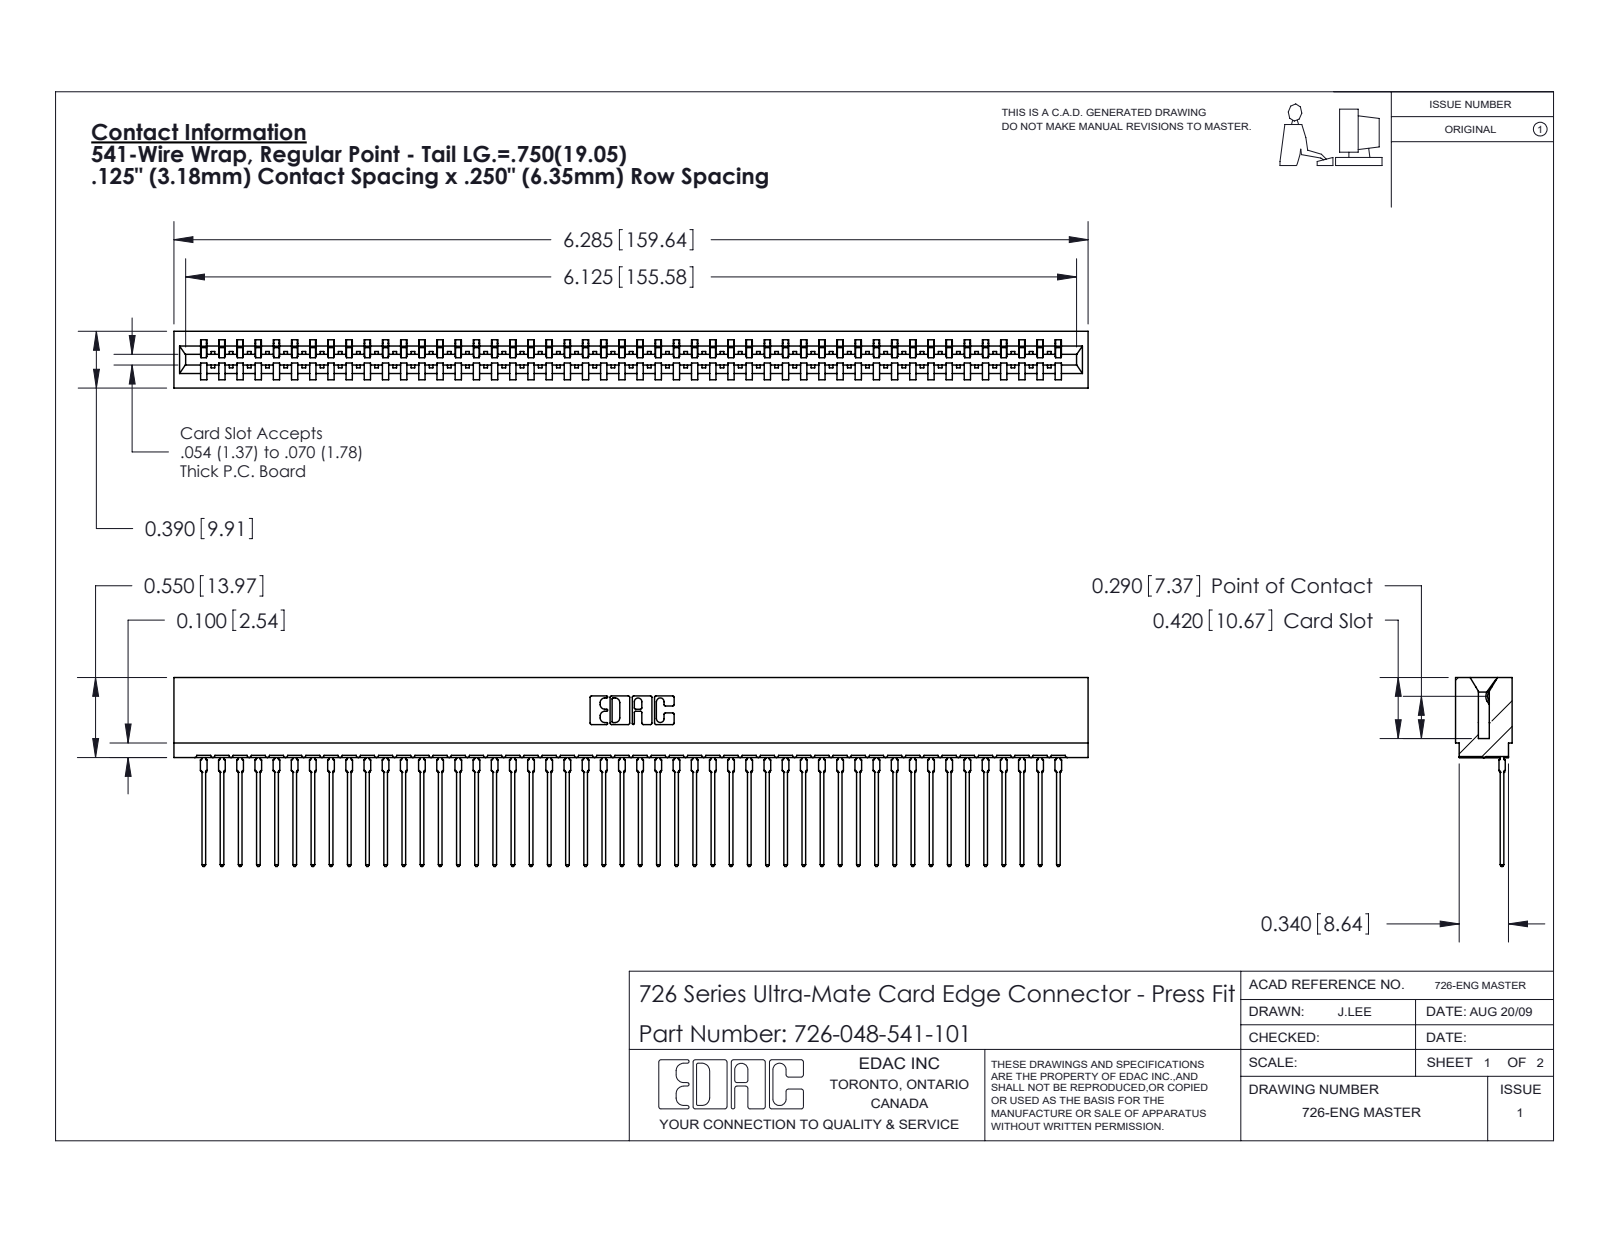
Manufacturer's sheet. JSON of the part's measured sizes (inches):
{"part_name": "726 Part_.515 Slot Depth - 01; 726-048-541-101; 746-292-001_541", "step_written_by": "SolidWorks 2020 (CONFIG_CONTROL_DESIGN)", "units": "inches", "bodies": {"solids": 49, "faces": 5281, "planar": 3079, "cylindrical": 954, "other": 1248}, "overall_size": [6.285, 1.299, 0.39], "volume_in3": 0.882, "surface_area_in2": 36.09, "partial_cylinders_radius": [[0.021, 96], [0.015, 49], [0.01, 22], [0.007, 6], [0.031, 6], [0.005, 4], [0.011, 4], [0.026, 3]], "face_to_face_distances": [0.057, 0.333, 0.39, 0.025, 0.307, 0.25, 0.083, 0.275, 0.365, 0.032]}
